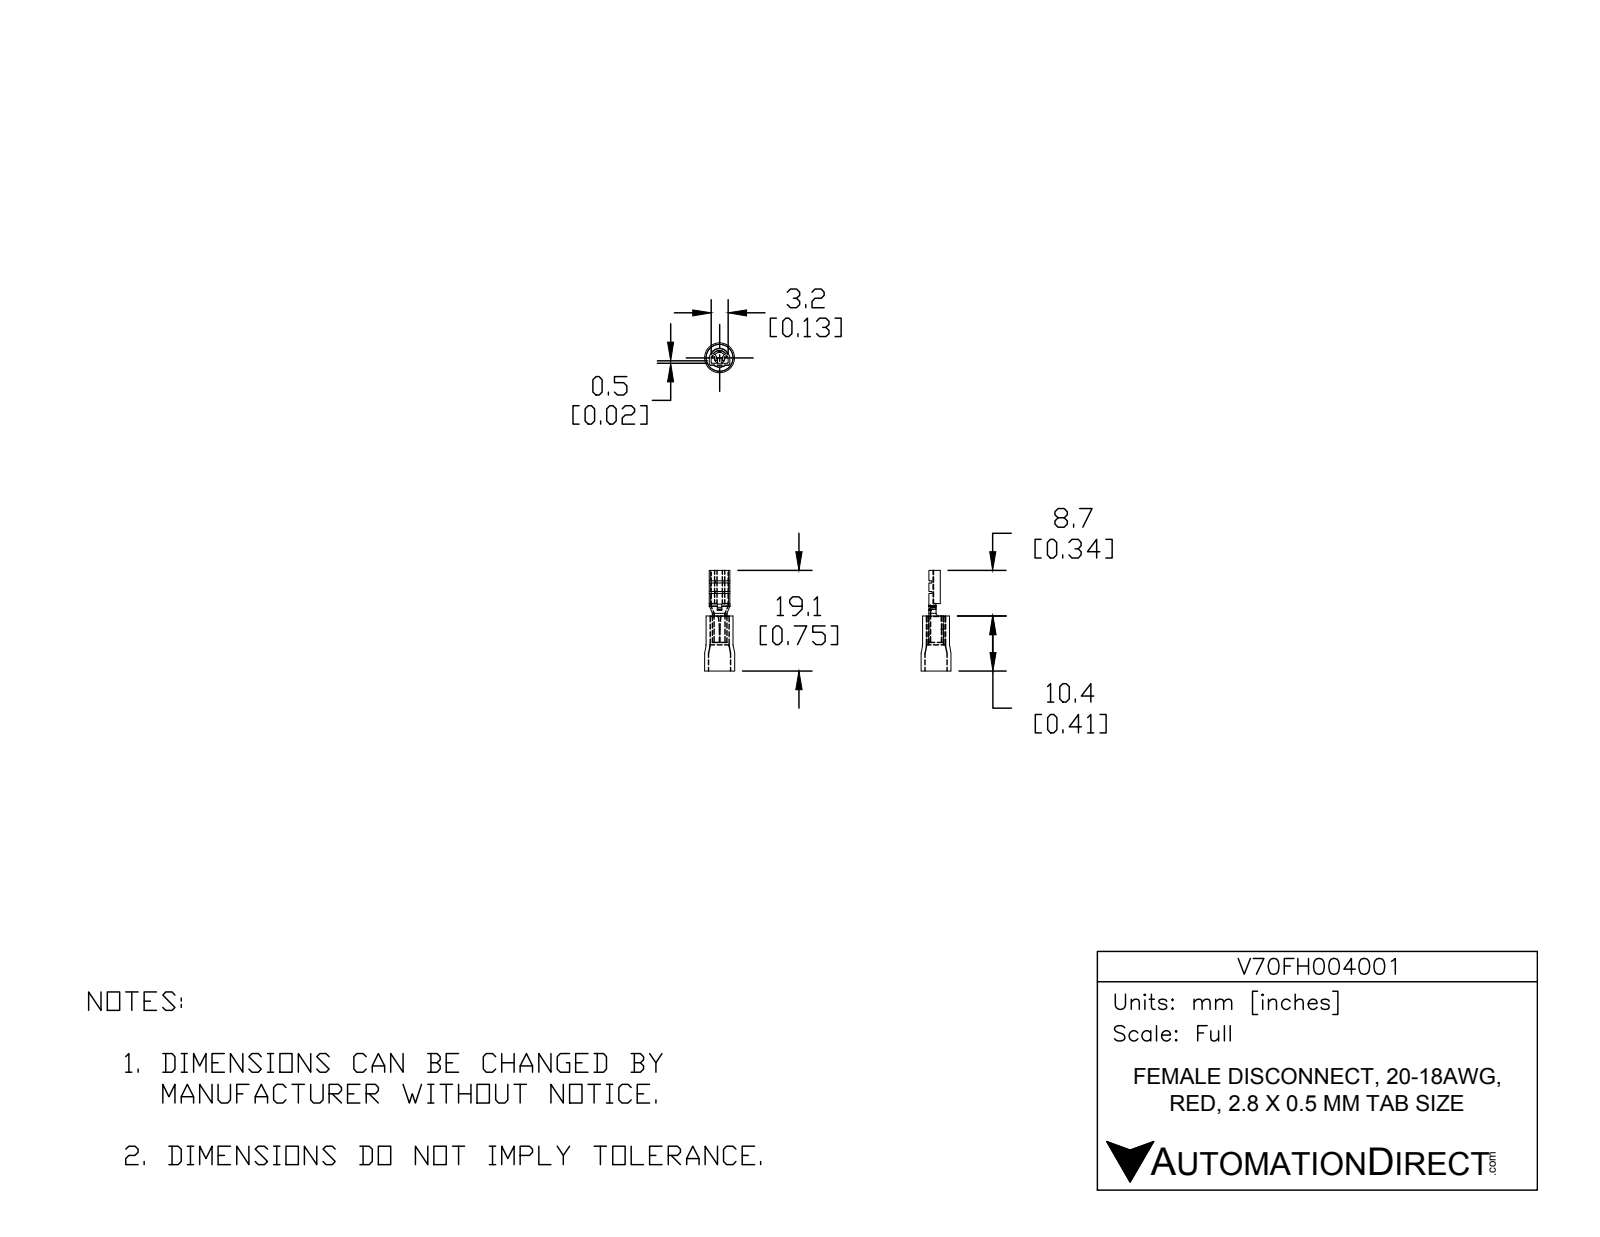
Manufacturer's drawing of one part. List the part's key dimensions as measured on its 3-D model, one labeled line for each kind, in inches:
Part name (STEP PRODUCT): V70FH004001
STEP written by: SolidWorks 2017 (AUTOMOTIVE_DESIGN)
Units: inches
Bodies: 3 solids, 121 faces (49 planar, 38 cylindrical, 34 other)
Overall size (bounding box): 0.751 × 0.224 × 0.224
Volume: 0.011 in³ · Surface area: 1.18 in²
Round holes (diameter × count): ⌀0.081 ×1, ⌀0.109 ×1, ⌀0.142 ×1, ⌀0.165 ×1
Round bosses / shafts (diameter × count): ⌀0.224 ×1, ⌀0.201 ×1, ⌀0.137 ×1, ⌀0.108 ×1
Partial cylindrical surfaces — rounded edges, fillets, slot ends (radius × count): R0.005 ×2, R0.01 ×2, R0.013 ×2, R0.026 ×2, R0.619 ×2, R0.014 ×1, R0.02 ×1, R0.028 ×1
Main face-to-face distances: 0.014, 0.014, 0.139, 0.41, 0.154, 0.125, 0.079, 0.751, 0.341, 0.406
